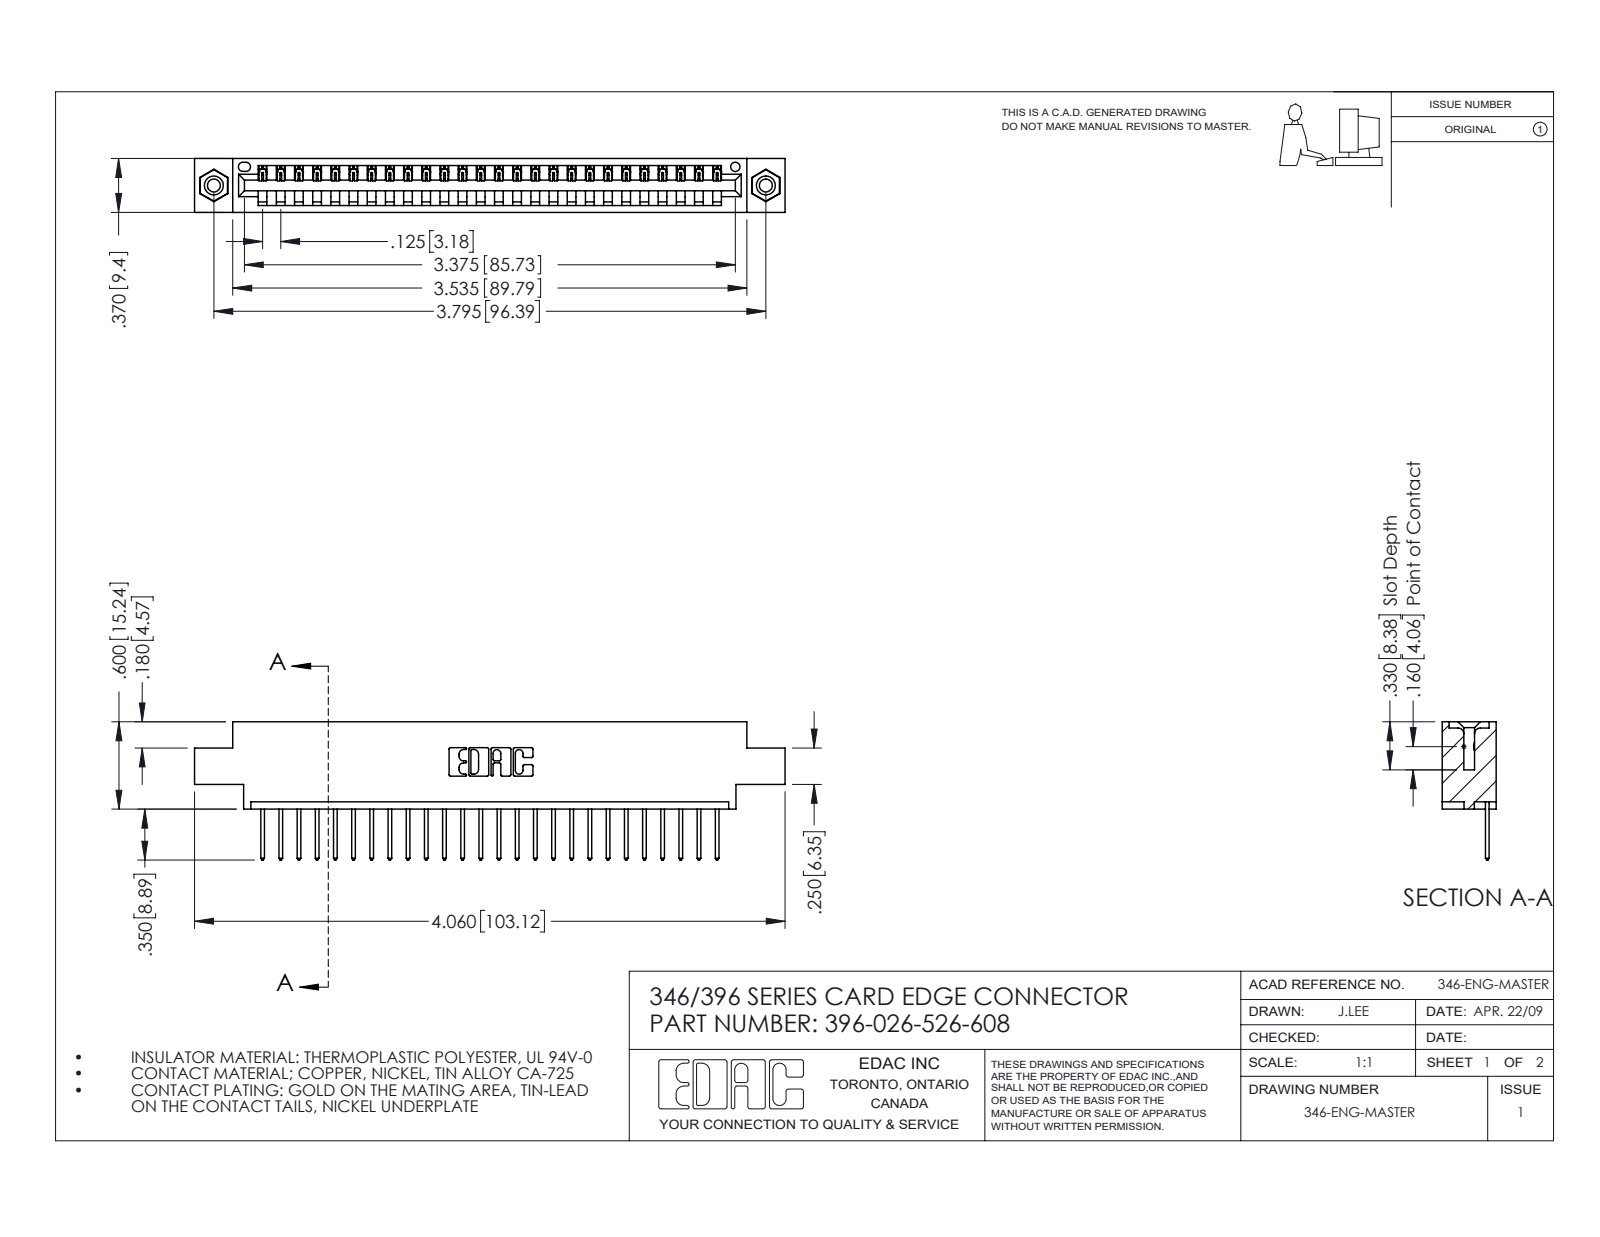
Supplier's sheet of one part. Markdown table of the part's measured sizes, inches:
| quantity | value |
| --- | --- |
| part name | 346 Part_0.170 Offset - 0.156 Dia-TI; 396-026-526-608; 345-292-001_345-293-126; 345-250-001_345-250-003-102 |
| STEP written by | SolidWorks 2016 (CONFIG_CONTROL_DESIGN) |
| units | inches |
| bodies | 29 solids, 1694 faces (1152 planar, 526 cylindrical, 16 other) |
| overall size | 4.06 × 0.95 × 0.37 |
| volume | 0.585 in³ |
| surface area | 18.53 in² |
| round holes (diameter × count) | 0.089 × 2, 0.125 × 2, 0.156 × 2, 0.064 × 1 |
| round bosses / shafts (diameter × count) | 0.155 × 2 |
| partial cylindrical surfaces (radius × count) | 0.006 × 52, 0.01 × 52, 0.01 × 22, 0.007 × 6, 0.031 × 6, 0.026 × 3, 0.031 × 2, 0.04 × 2 |
| main face-to-face distances | 0.048, 0.322, 0.37, 0.25, 0.072, 0.298, 0.025, 0.222, 0.148, 0.1 |
| hole center spacings | 0.246, 3.587, 3.795 |
